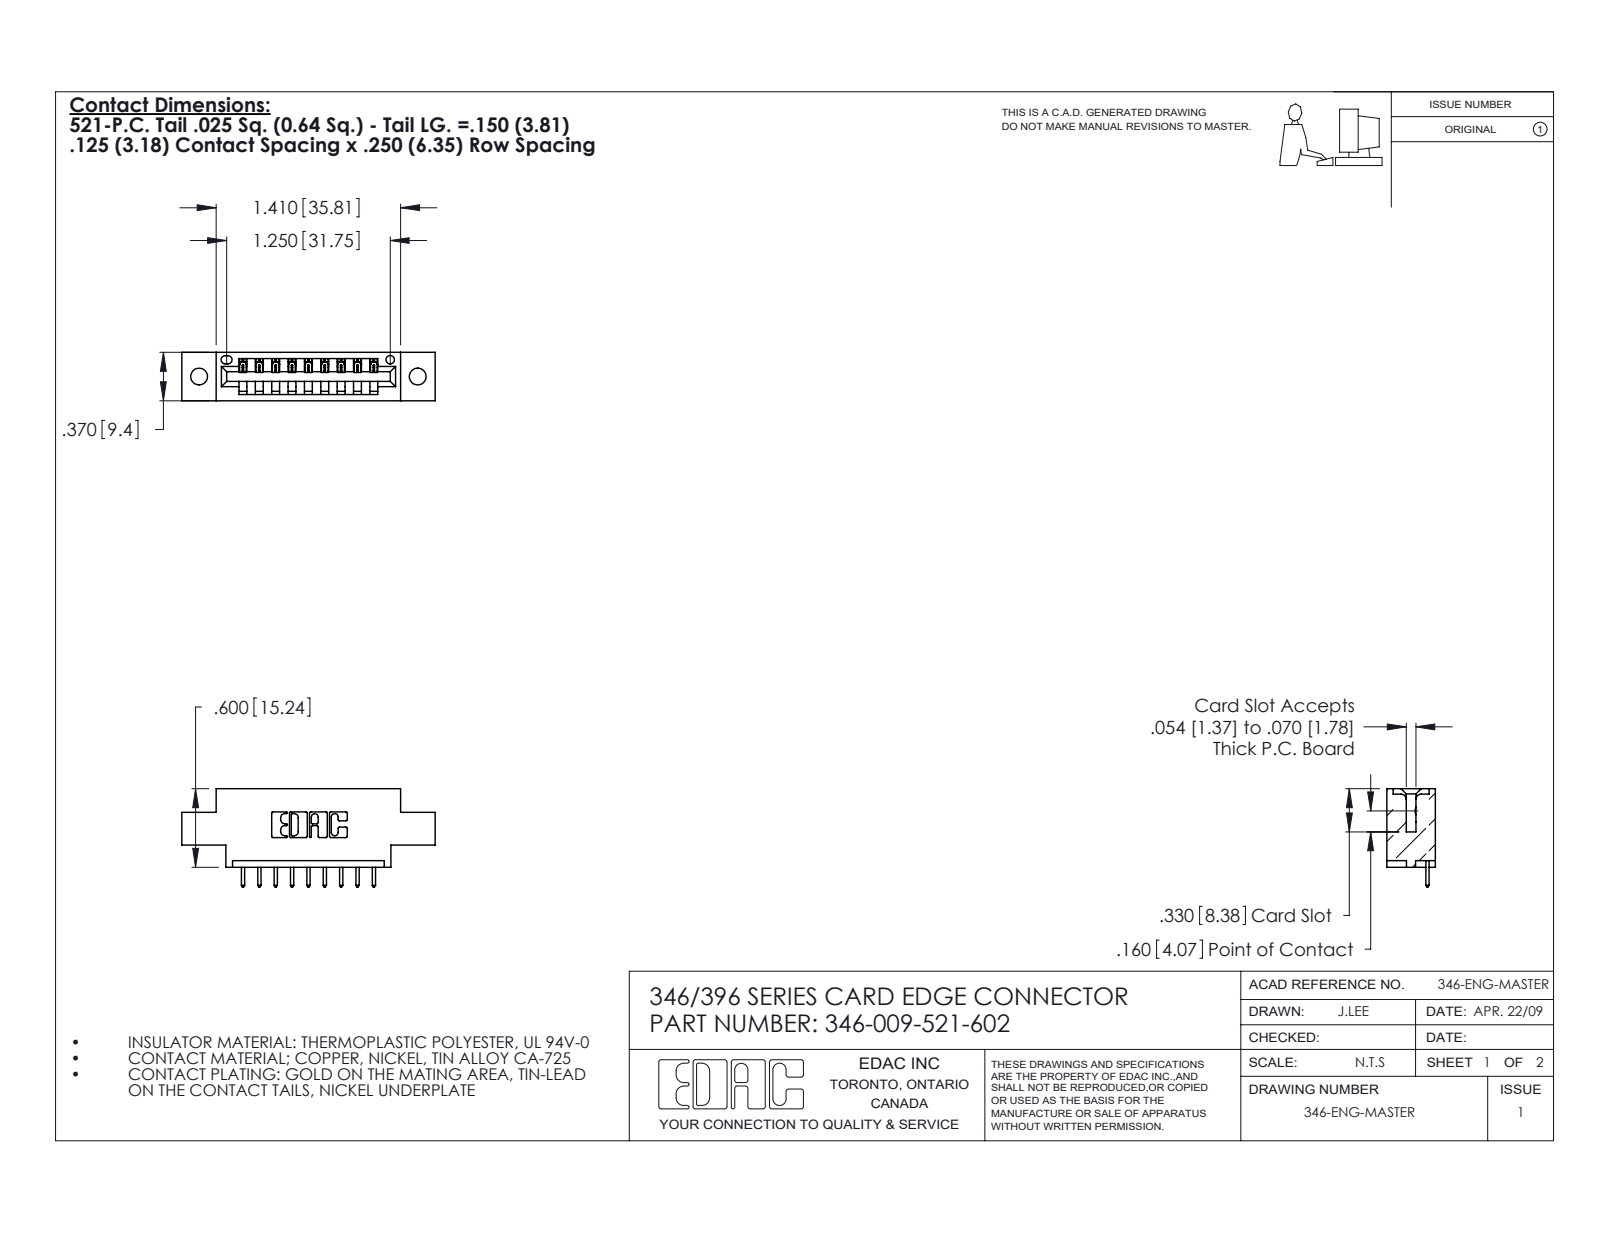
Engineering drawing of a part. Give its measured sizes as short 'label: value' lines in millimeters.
name: 346 Part_0.170 Offset - 0.128 Dia; 346-009-521-602; 345-292-001_345-293-121
written by: SolidWorks 2020 (CONFIG_CONTROL_DESIGN)
unit: mm
bodies: 10 solids, 648 faces (440 planar, 208 cylindrical, 0 other)
size: 49.1 × 19.1 × 9.4
volume: 4 260 mm³; area: 4 756 mm²
holes: 2× ⌀3.3, 1× ⌀1.6
rounds: 22× R0.3, 18× R0.2, 18× R0.3, 6× R0.2, 6× R0.8, 3× R0.7, 2× R0.8, 2× R1
face distances: 6.4, 9.4, 1.2, 8.2, 3.8, 5.6, 2.5, 4.4, 1.8, 7.6
hole spacings: 6.2, 37.2, 42.4
